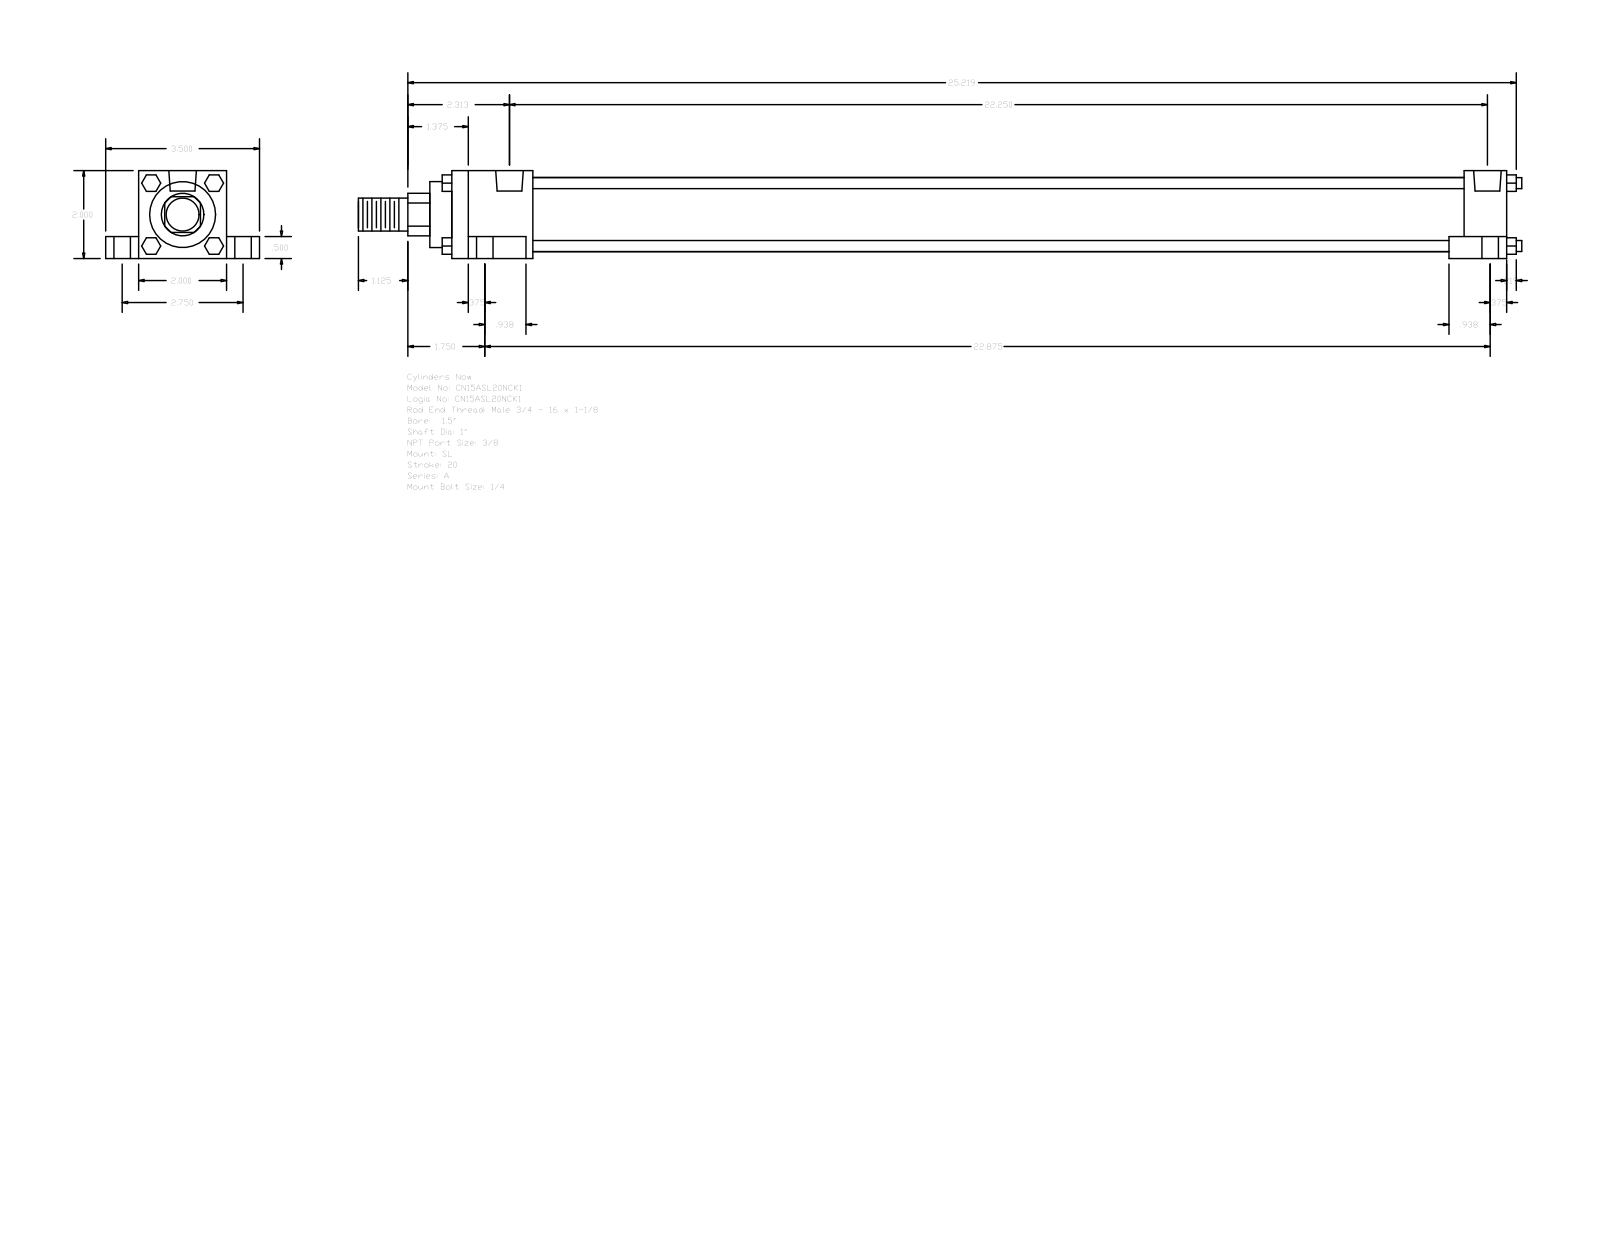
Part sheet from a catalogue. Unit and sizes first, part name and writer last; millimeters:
Units: millimetres
Overall size (bounding box): 672.31 × 88.9 × 50.8
Round holes (diameter × count): ⌀5.56 ×4, ⌀9.53 ×4, ⌀15.88 ×4, ⌀15.93 ×2
Round bosses / shafts (diameter × count): ⌀6.35 ×4, ⌀42.93 ×1, ⌀38.1 ×1, ⌀25.4 ×1, ⌀19.05 ×1
Partial cylindrical surfaces — rounded edges, fillets, slot ends (radius × count): R12.29 ×1
Main face-to-face distances: 50.8, 12.7, 38.1, 19.05, 69.85, 9.52, 609.6, 33.34, 584.99, 24.61
Hole centre spacings: 3.97, 34.96, 35.36, 37.73, 39.41, 69.84, 557.21, 561.18
Bodies: 0 solids, 148 faces (112 planar, 36 cylindrical, 0 other)
Part name (STEP PRODUCT): A_SL__0150_1
STEP written by: GSSL Pune (CONFIG_CONTROL_DESIGN)
